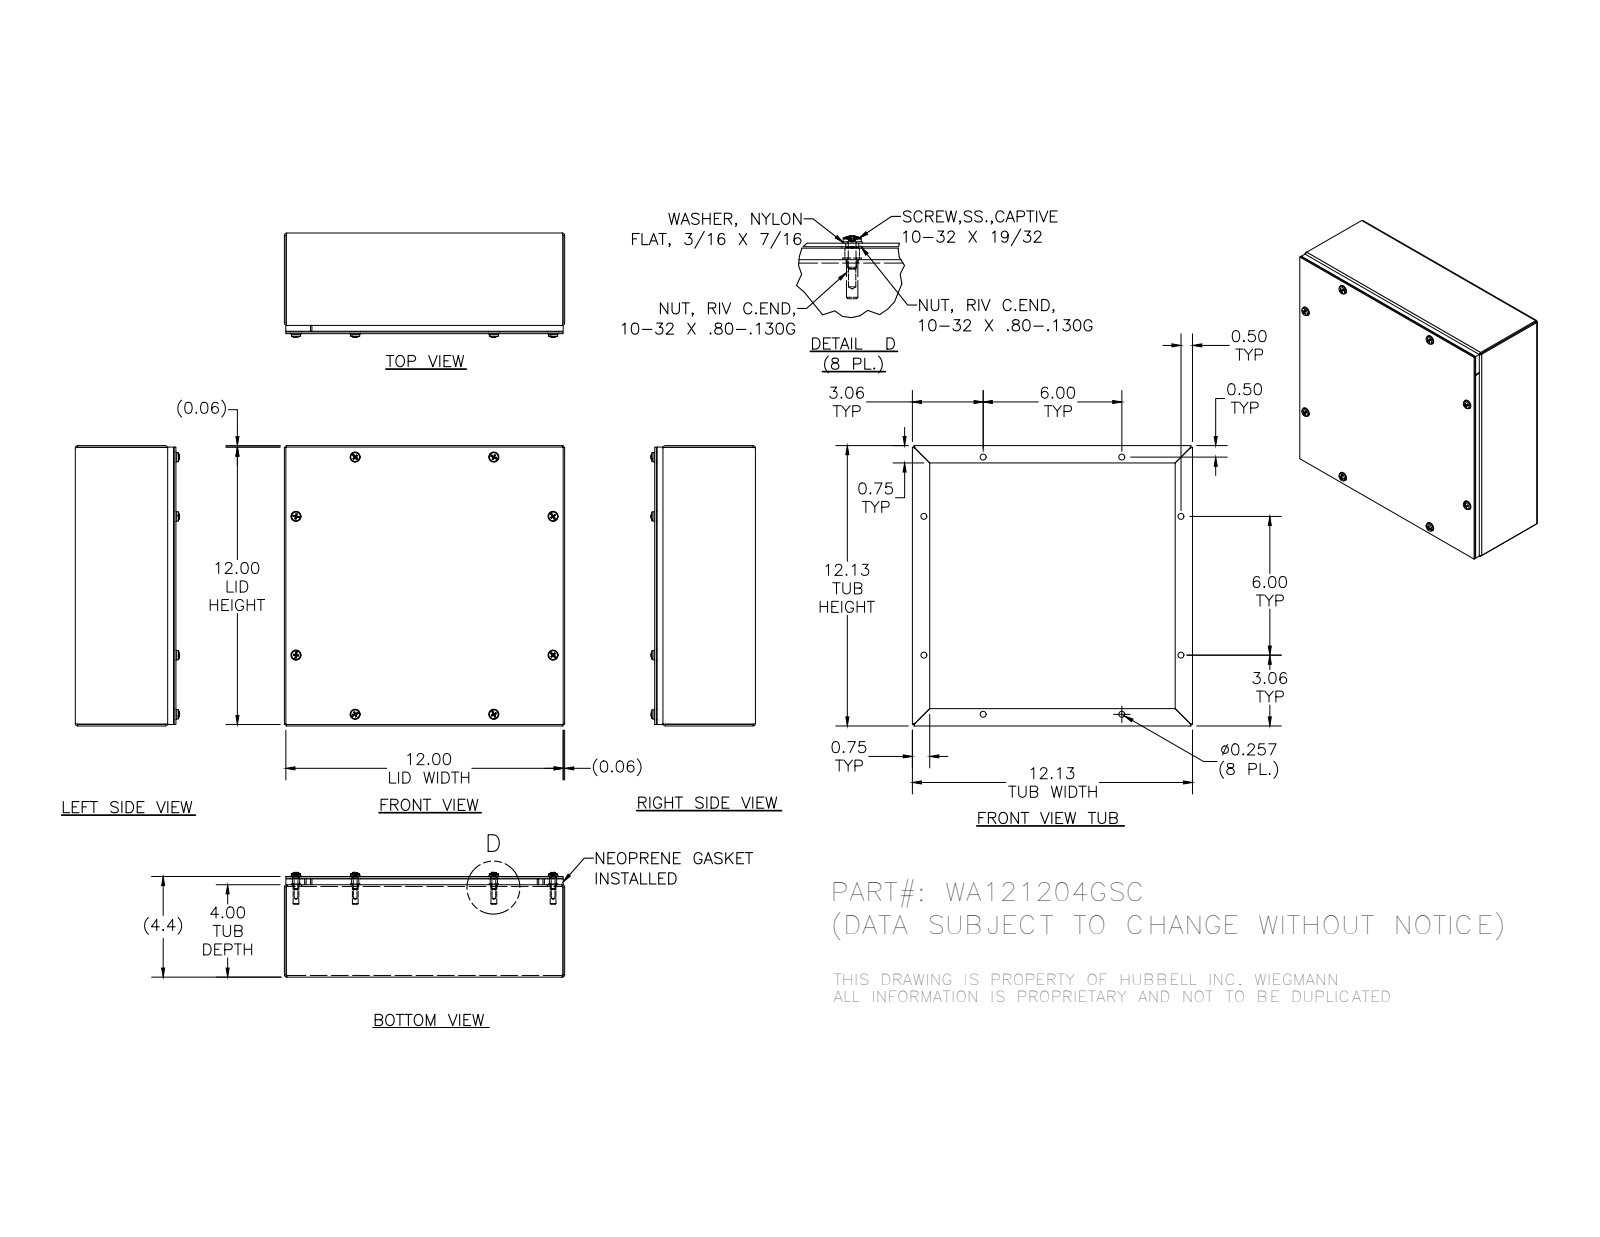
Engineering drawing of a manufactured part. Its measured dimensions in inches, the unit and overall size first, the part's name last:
Units: inches
Overall size (bounding box): 12.125 × 12.125 × 4.511
Round holes (diameter × count): ⌀0.156 ×8, ⌀0.188 ×8, ⌀0.196 ×8, ⌀0.257 ×8, ⌀0.278 ×8, ⌀0.281 ×8, ⌀0.313 ×8
Round bosses / shafts (diameter × count): ⌀0.453 ×8, ⌀0.437 ×8, ⌀0.406 ×8, ⌀0.248 ×8, ⌀0.167 ×8
Partial cylindrical surfaces — rounded edges, fillets, slot ends (radius × count): R0.031 ×8, R0.089 ×8, R0.105 ×8
Main face-to-face distances: 0.074, 4.282, 12.051, 4.356, 4.208, 0.356, 3.926, 12.125, 11.977, 0.282
Hole centre spacings: 6, 8.938, 8.937, 3.624, 8.937, 12.109, 11.124, 11.125
Volume: 47.54 in³ · Surface area: 1 146 in²
Bodies: 36 solids, 892 faces (420 planar, 240 cylindrical, 232 other)
Part name (STEP PRODUCT): 39077; WA121204GSCBKP; WA121204GSC; WA1212GSC_LP (+4 more)
STEP written by: SolidWorks 2014 (AUTOMOTIVE_DESIGN)
